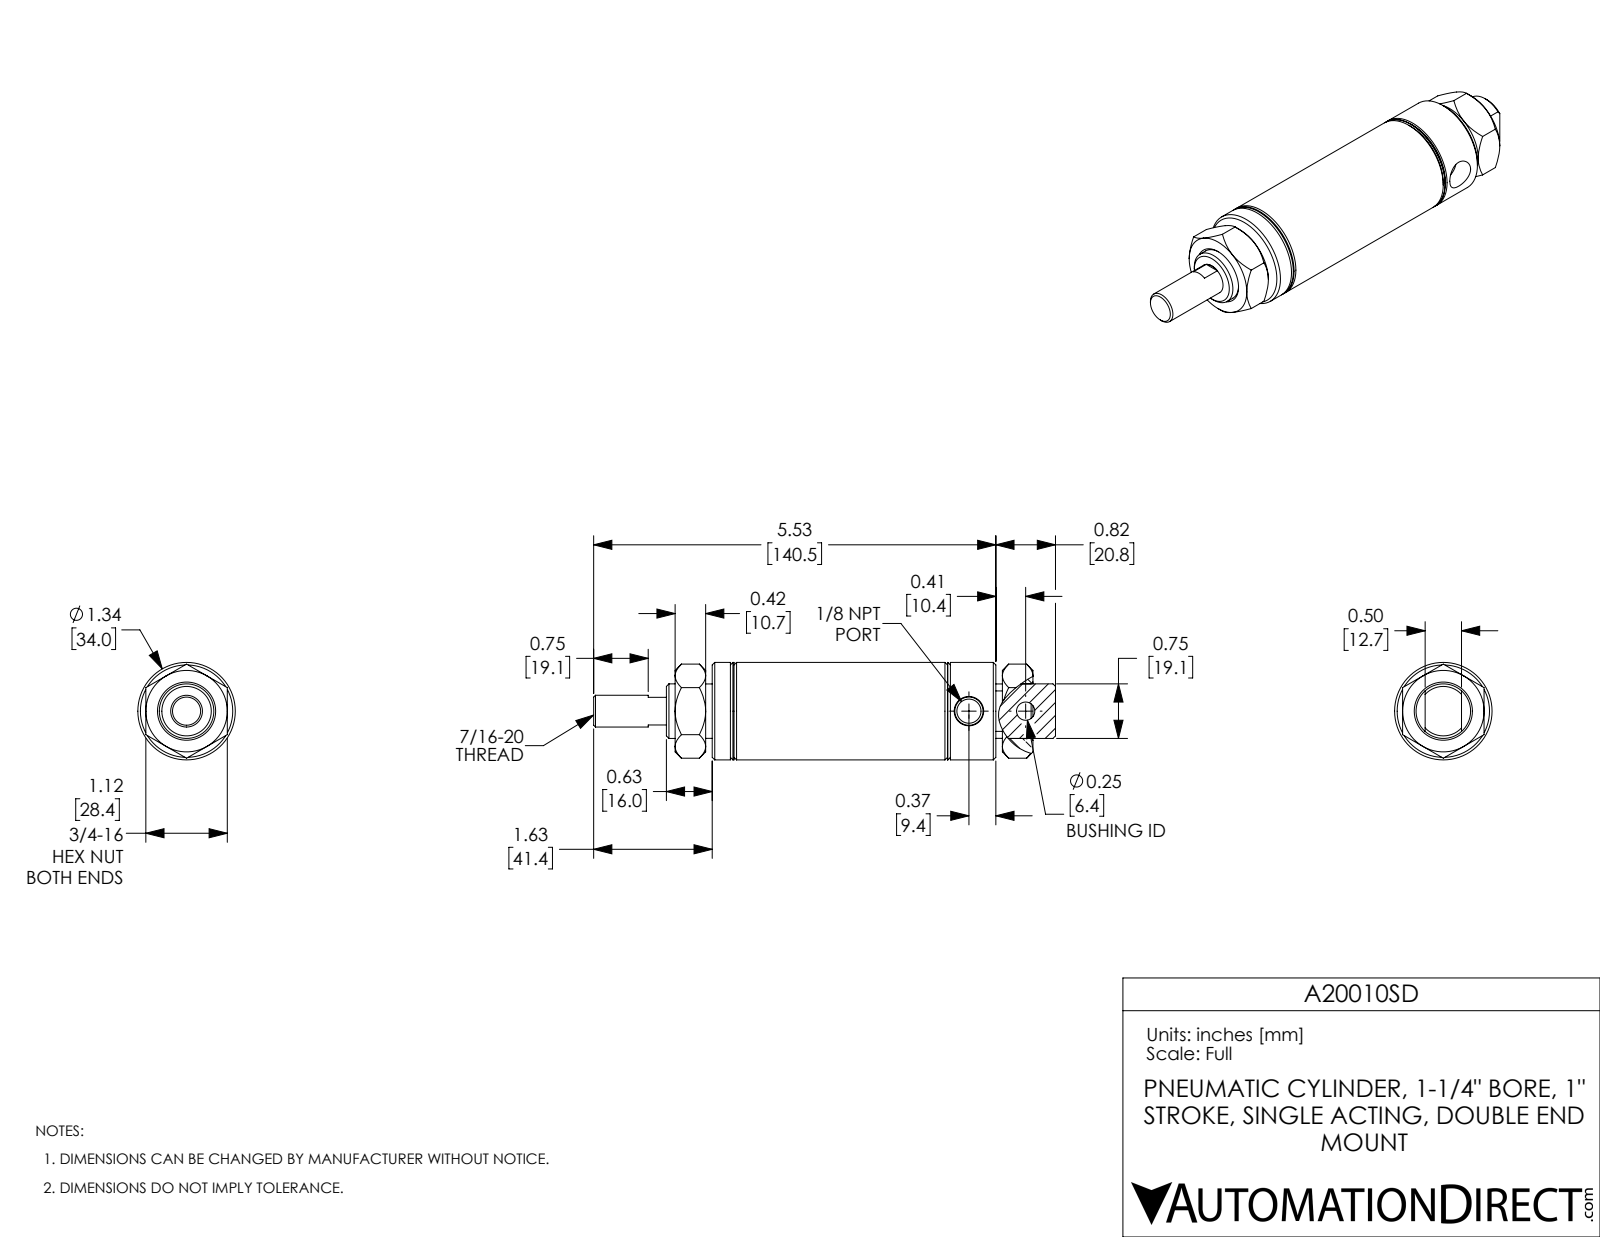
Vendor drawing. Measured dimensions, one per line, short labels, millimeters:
name: A20010SD-MainBody; A20010SD; A20010SD_Mounting Nut_D-3556; A20010SD-P-Rod
written by: SolidWorks 2017 (AUTOMOTIVE_DESIGN)
unit: mm
bodies: 4 solids, 129 faces (41 planar, 34 cylindrical, 54 other)
size: 161.3 × 34 × 34
volume: 91 190 mm³; area: 33 230 mm²
holes: 1× ⌀6.4, 1× ⌀8.4, 1× ⌀11.1, 1× ⌀19.1, 1× ⌀31.8
bosses: 1× ⌀34, 1× ⌀19
face distances: 30.5, 68.6, 12.7, 28.4, 25.4, 7.9, 38.1, 10.7, 114.3, 20.6
hole spacings: 19.8
